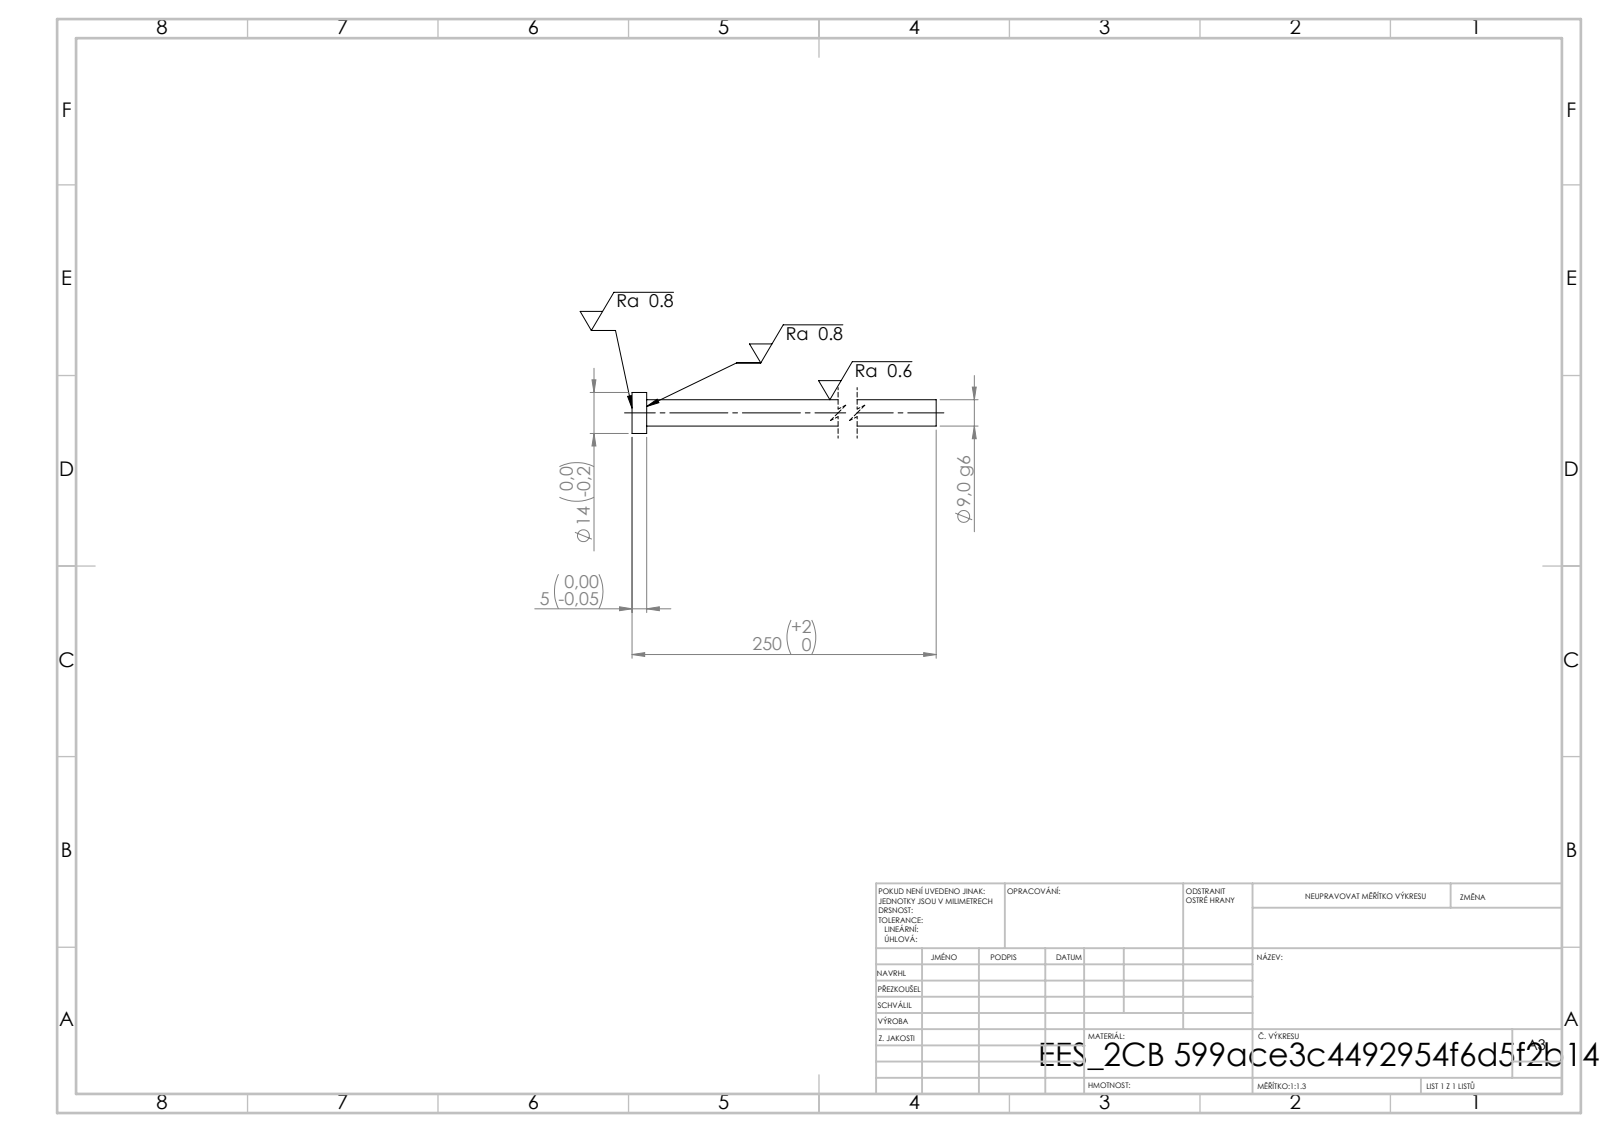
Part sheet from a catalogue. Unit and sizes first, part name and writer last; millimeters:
Units: millimetres
Overall size (bounding box): 250 × 14 × 14
Round bosses / shafts (diameter × count): ⌀14 ×1, ⌀9 ×1
Main face-to-face distances: 5, 250, 245
Volume: 16 356 mm³ · Surface area: 7 455 mm²
Bodies: 1 solid, 7 faces (3 planar, 4 cylindrical, 0 other)
STEP written by: SolidWorks 2019 (CONFIG_CONTROL_DESIGN)
